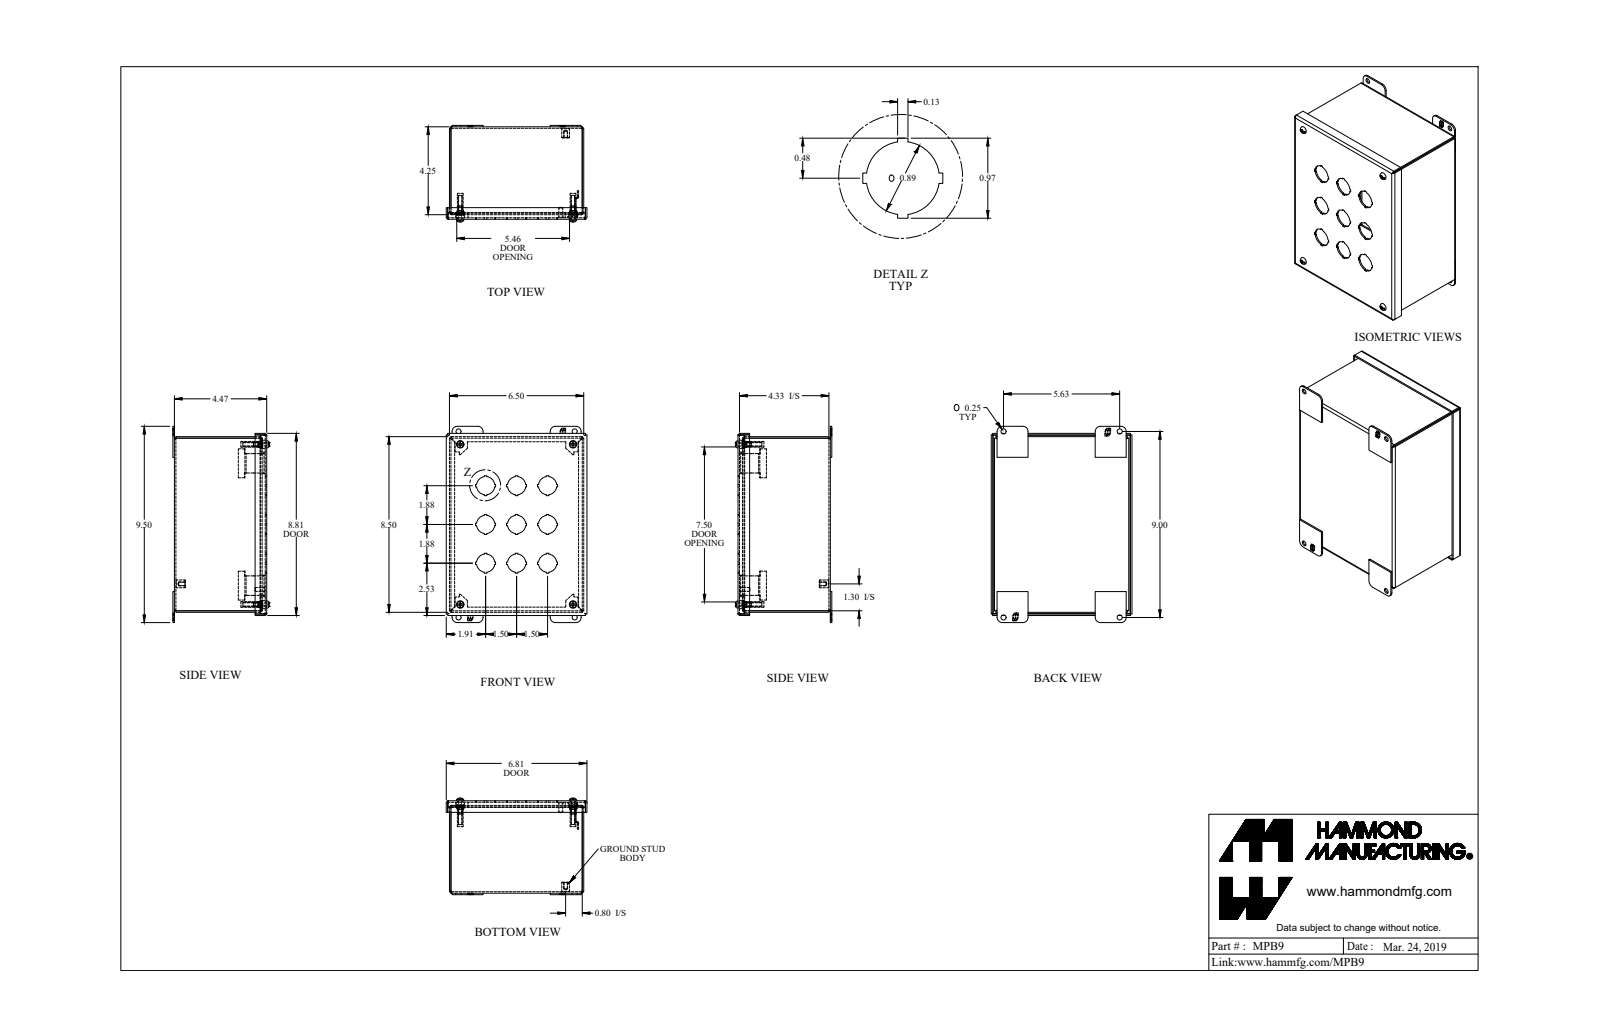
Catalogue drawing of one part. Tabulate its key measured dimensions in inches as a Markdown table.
| quantity | value |
| --- | --- |
| part name | MPB9 |
| STEP written by | SolidWorks 2018 (AUTOMOTIVE_DESIGN) |
| units | inches |
| bodies | 23 solids, 859 faces (607 planar, 196 cylindrical, 56 other) |
| overall size | 9.5 × 6.813 × 4.671 |
| volume | 22.03 in³ |
| surface area | 588.2 in² |
| round holes (diameter × count) | 0.886 × 9, 0.25 × 8, 0.159 × 4, 0.406 × 4, 0.156 × 1 |
| round bosses / shafts (diameter × count) | 0.39 × 4, 0.275 × 4, 0.19 × 4, 0.148 × 4, 0.375 × 1, 0.25 × 1, 0.188 × 1 |
| partial cylindrical surfaces (radius × count) | 0.036 × 12, 0.108 × 12, 0.25 × 8, 0.029 × 4, 0.086 × 4, 0.16 × 4, 0.171 × 4 |
| main face-to-face distances | 0.072, 4.4, 6.428, 4.472, 4.328, 8.428, 6.5, 6.356, 8.5, 8.356 |
| hole center spacings | 2.401, 5.461, 5.578, 1.5, 5.737, 0.63, 0.631, 3.538 |
